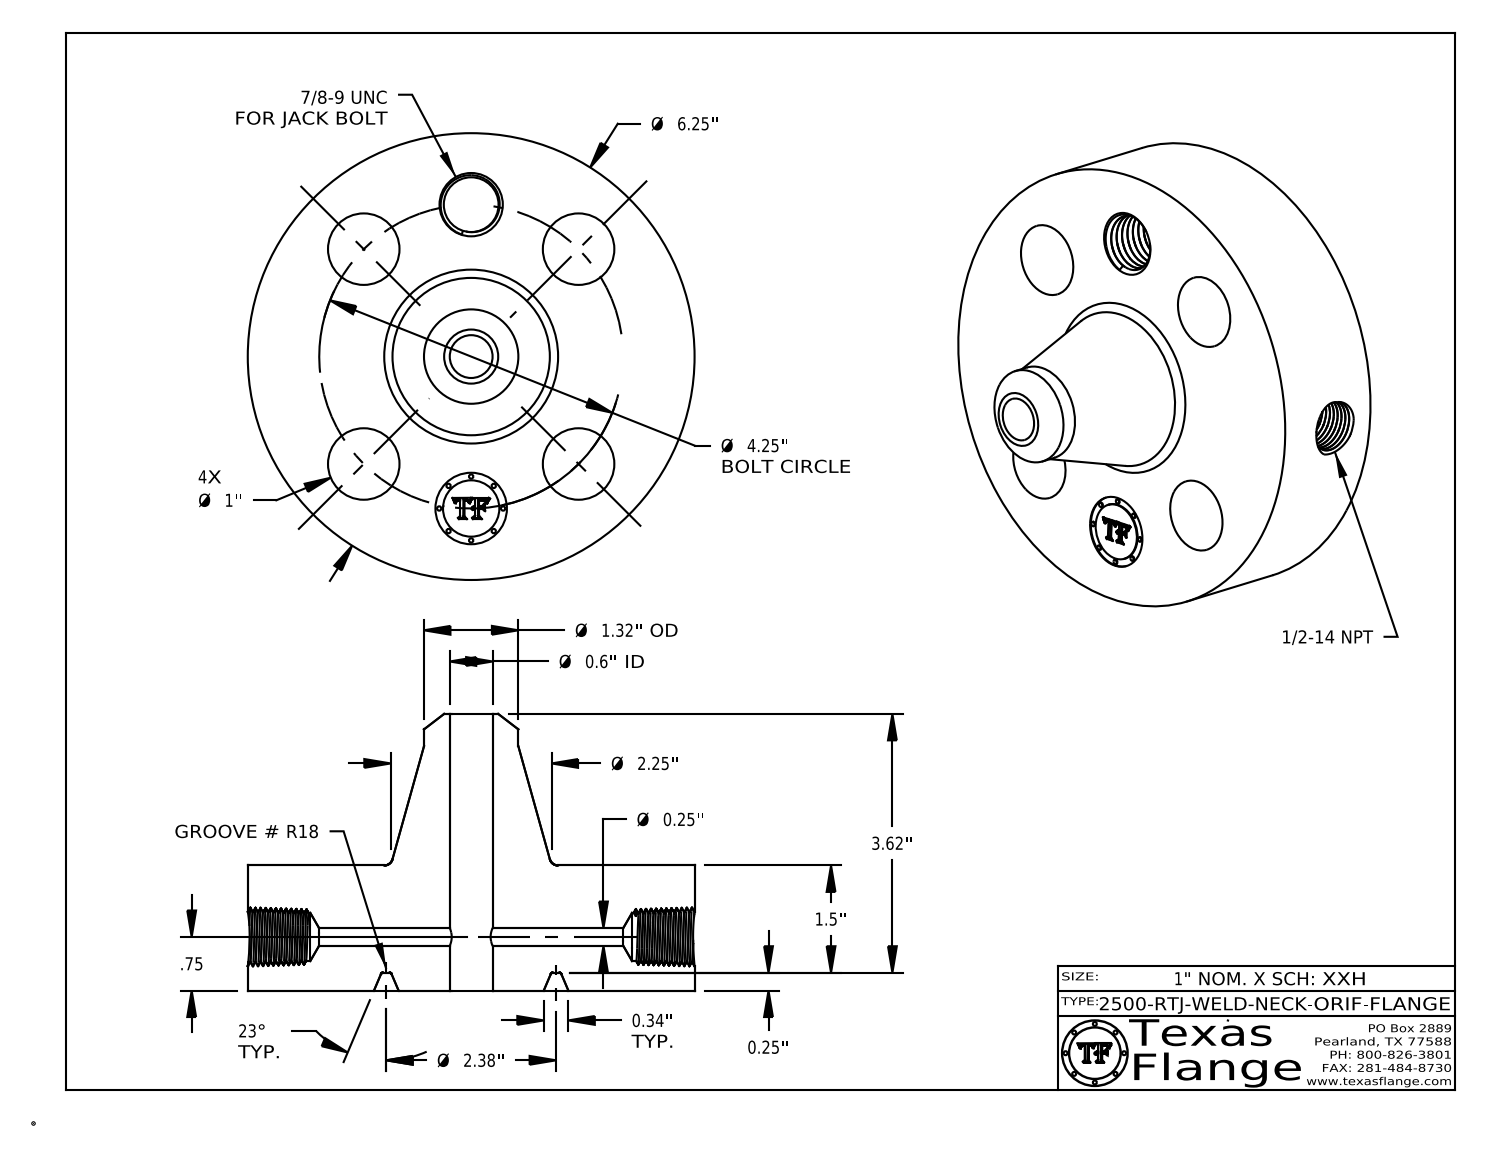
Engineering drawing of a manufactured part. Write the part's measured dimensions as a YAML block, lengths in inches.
part_name: "2500-RTJ-WELD-NECK"
step_written_by: "CATIA V5 STEP AP214 (AUTOMOTIVE_DESIGN)"
units: inches
bodies: {solids: 1, faces: 773, planar: 370, cylindrical: 85, other: 318}
overall_size: [6.25, 6.25, 3.87]
volume: 49.56
surface_area: 143.8
round_holes:
  - {diameter: 1, count: 5}
  - {diameter: 0.25, count: 1}
  - {diameter: 0.599, count: 1}
  - {diameter: 0.672, count: 1}
  - {diameter: 0.766, count: 1}
round_bosses_or_shafts:
  - {diameter: 0.061, count: 8}
  - {diameter: 6.25, count: 1}
  - {diameter: 1.32, count: 1}
  - {diameter: 0.788, count: 1}
face_to_face_distances: [1.75, 0.25, 1.5, 0.015, 1.735, 1.485, 3.87, 3.62, 2.135, 2.12]
hole_center_spacings: [2.125, 1.626, 3.006, 3.927, 4.25]
